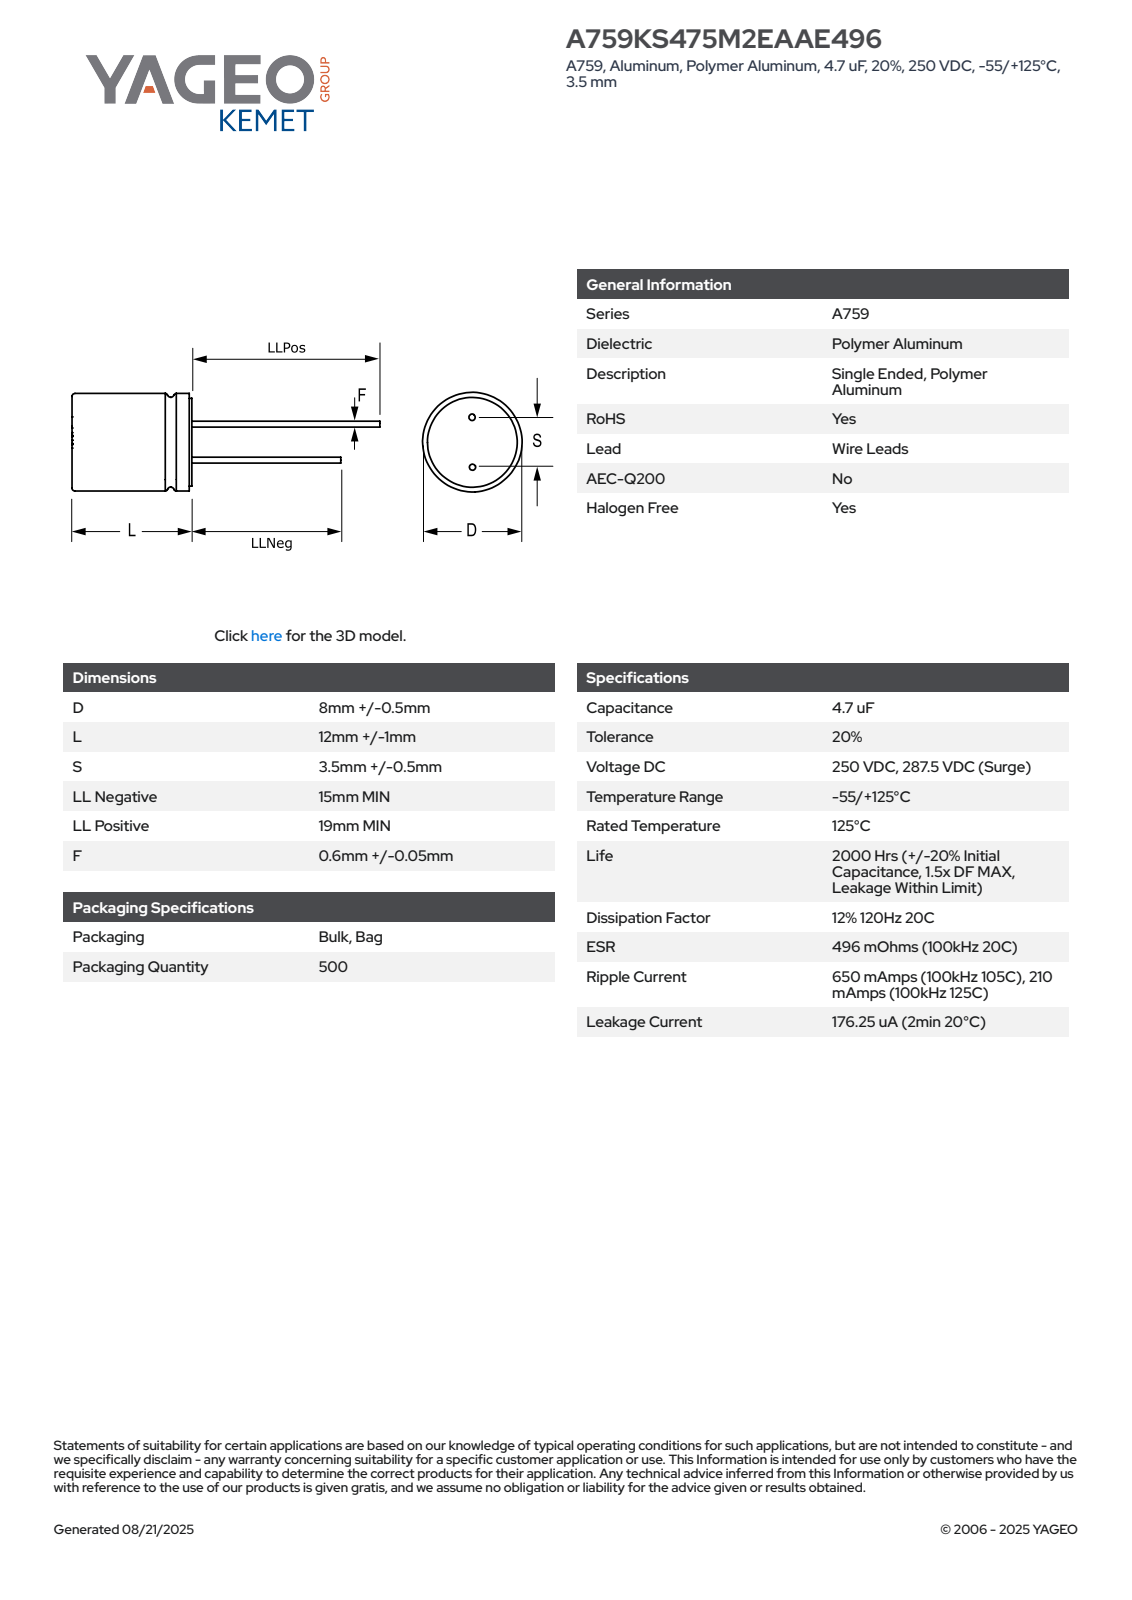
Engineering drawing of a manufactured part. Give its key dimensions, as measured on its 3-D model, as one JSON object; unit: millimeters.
{"part_name": "CAR_KP_8X12_D8.5L13S3.5F0.65", "step_written_by": "SolidWorks 2014 (AUTOMOTIVE_DESIGN)", "units": "millimeters", "bodies": {"solids": 4, "faces": 75, "planar": 61, "cylindrical": 8, "other": 6}, "overall_size": [32.01, 8.5, 8.5], "volume_mm3": 742, "surface_area_mm2": 543, "round_bosses_or_shafts": [[0.65, 2], [8.5, 1]], "face_to_face_distances": [13, 13.01, 28.01, 32.01, 28, 32, 15, 19, 4, 0.93]}
